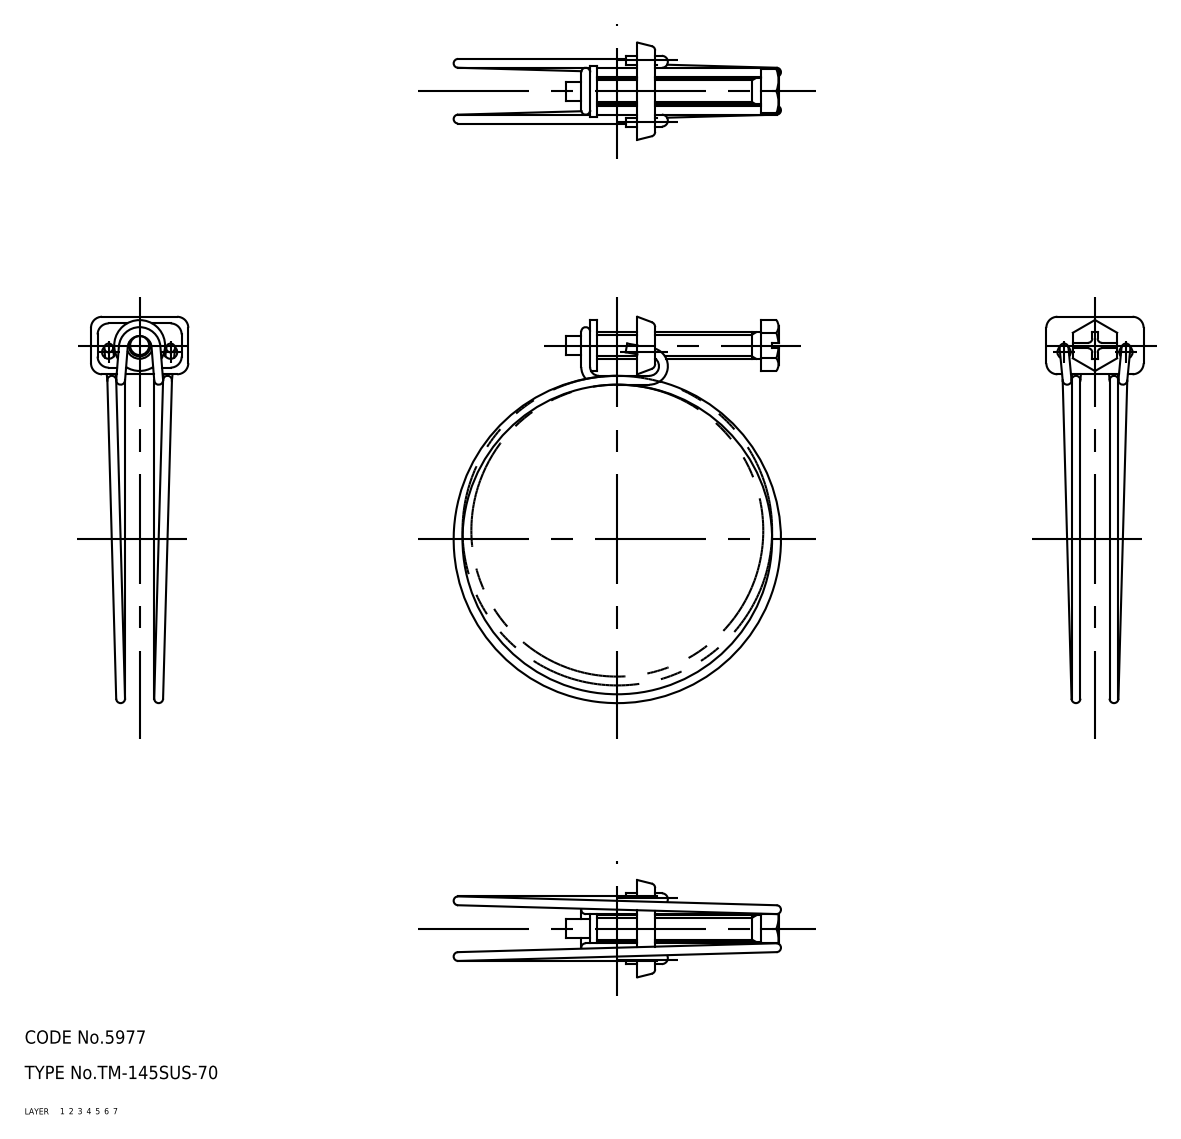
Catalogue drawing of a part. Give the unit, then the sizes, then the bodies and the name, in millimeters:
Units: millimetres
Overall size (bounding box): 87.35 × 74 × 22
Volume: 3 786 mm³ · Surface area: 5 507 mm²
Bodies: 3 solids, 119 faces (0 planar, 0 cylindrical, 119 other)
Part name (STEP PRODUCT): screw; holder; band; TM_145SUS_70_22702_36
STEP written by: CADfix (AUTOMOTIVE_DESIGN)
